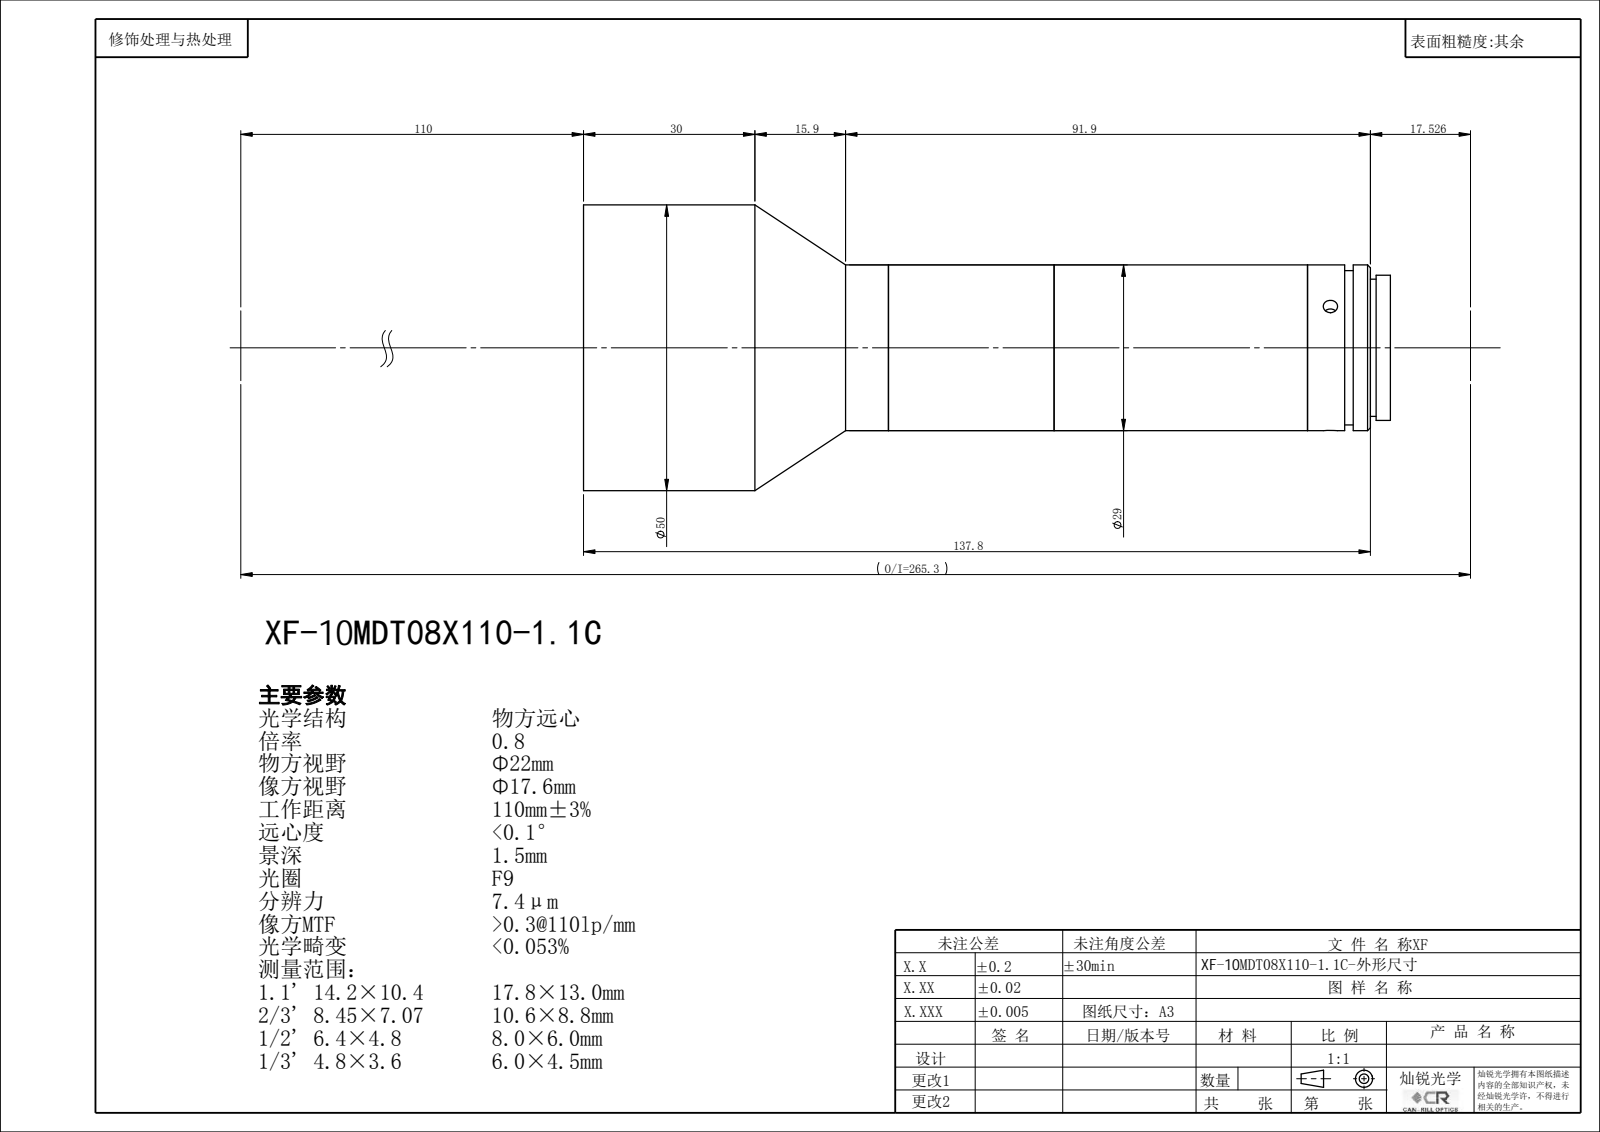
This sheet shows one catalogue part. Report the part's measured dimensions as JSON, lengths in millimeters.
{"part_name": "XF-5MDT08X110-1.1C", "step_written_by": "SolidWorks 2014 (CONFIG_CONTROL_DESIGN)", "units": "millimeters", "bodies": {"solids": 0, "faces": 62, "planar": 20, "cylindrical": 34, "other": 8}, "overall_size": [141.25, 50, 50], "round_holes": [[2.5, 3], [17, 1], [21.4, 1], [42, 1], [46, 1]], "round_bosses_or_shafts": [[50, 1], [29, 1], [27, 1], [25.4, 1], [24, 1], [20, 1]], "face_to_face_distances": [126.75, 4.17, 122.58, 5.5, 135.75, 131.58, 9, 6.5, 8, 133.58]}
